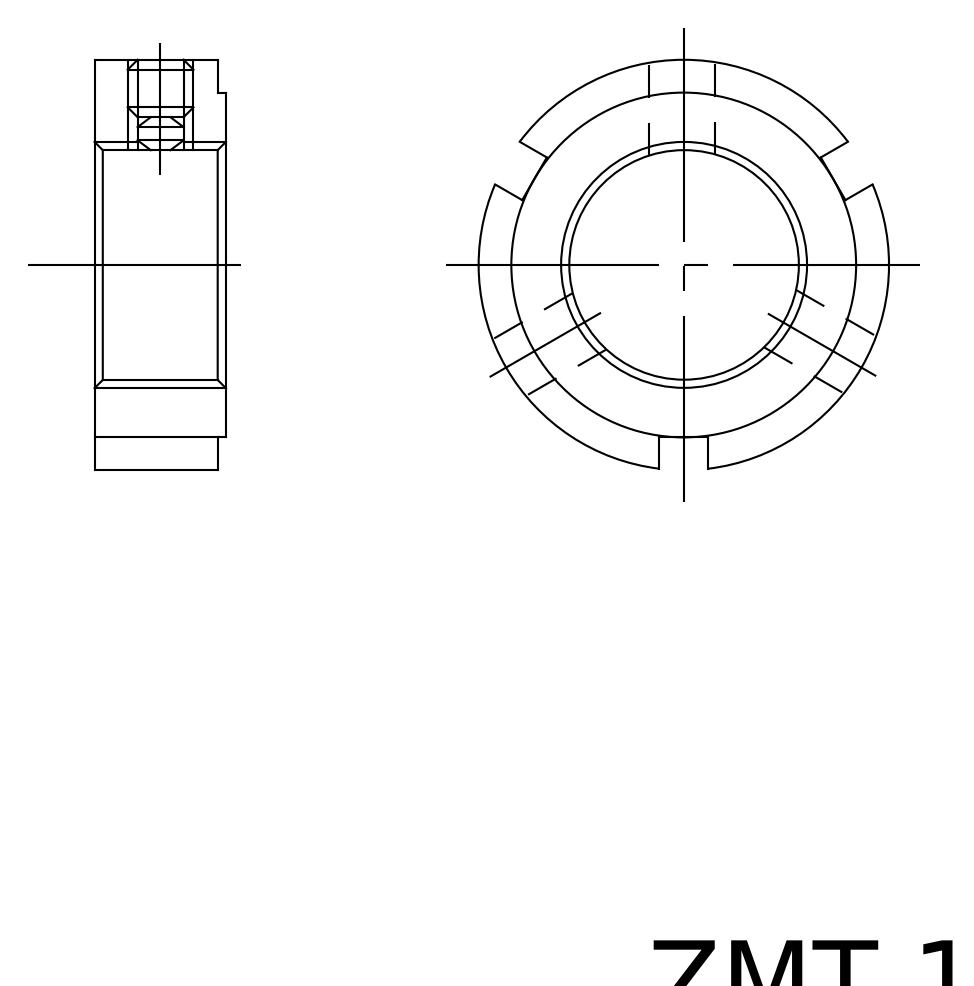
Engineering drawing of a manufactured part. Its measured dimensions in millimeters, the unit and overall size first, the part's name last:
Units: millimetres
Overall size (bounding box): 25 × 24.91 × 8
Round holes (diameter × count): ⌀3.24 ×3, ⌀15 ×1
Round bosses / shafts (diameter × count): ⌀25 ×1, ⌀21 ×1
Main face-to-face distances: 8, 0.5, 7.5, 3
Volume: 2 184 mm³ · Surface area: 1 782 mm²
Bodies: 1 solid, 22 faces (14 planar, 8 cylindrical, 0 other)
Part name (STEP PRODUCT): FKD ZMT 15
STEP written by: Autodesk Inventor 2011 (AUTOMOTIVE_DESIGN)
